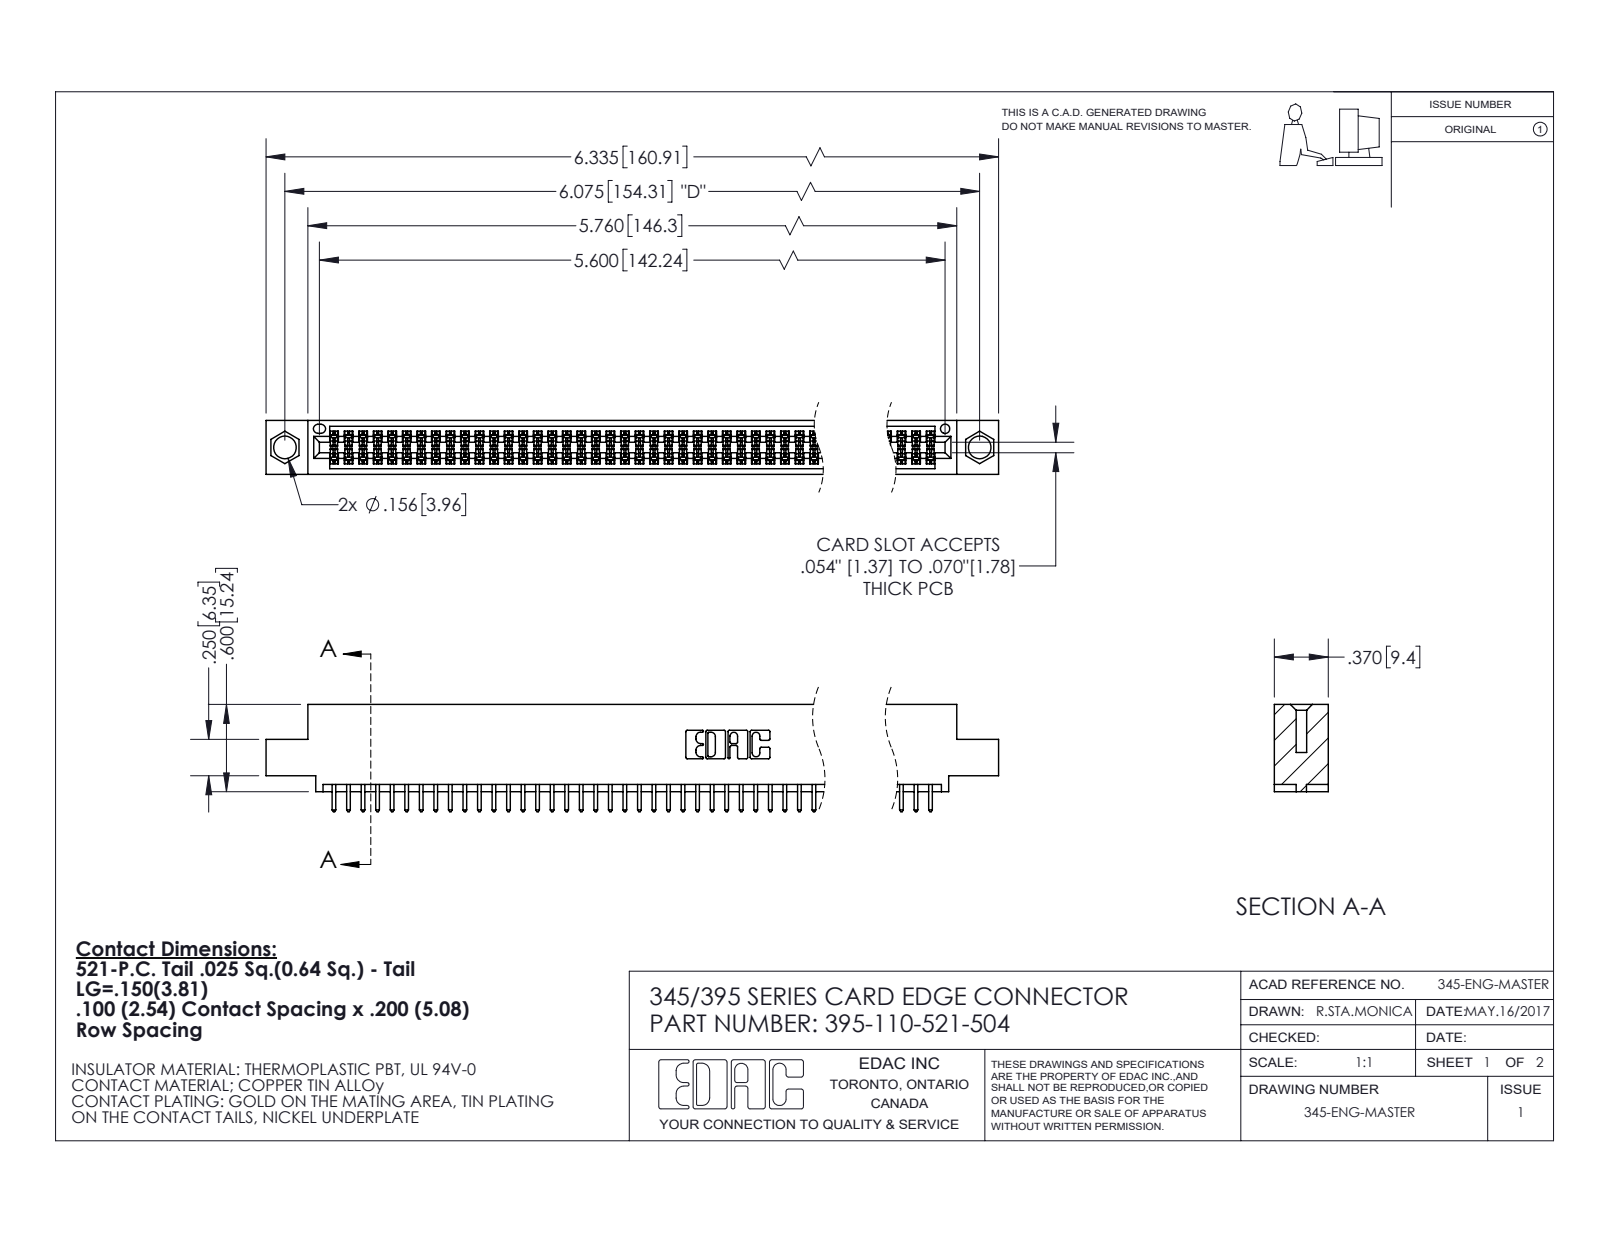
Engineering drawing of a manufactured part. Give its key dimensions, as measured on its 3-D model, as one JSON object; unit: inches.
{"part_name": "345 Part_0.110 Offset - 0.156 Dia-TI; 395-110-521-504; 345-292-001_345-293-121", "step_written_by": "SolidWorks 2020 (CONFIG_CONTROL_DESIGN)", "units": "inches", "bodies": {"solids": 111, "faces": 5644, "planar": 3728, "cylindrical": 1916, "other": 0}, "overall_size": [6.335, 0.737, 0.37], "volume_in3": 0.948, "surface_area_in2": 35.43, "round_holes": [[0.156, 2], [0.064, 1]], "partial_cylinders_radius": [[0.006, 165], [0.01, 110], [0.01, 22], [0.007, 6], [0.031, 6], [0.026, 3], [0.014, 2], [0.019, 2]], "face_to_face_distances": [0.298, 0.072, 0.2, 0.098, 0.272, 0.025, 0.37, 0.225, 0.175, 0.149], "hole_center_spacings": [0.27, 5.839, 6.075]}
